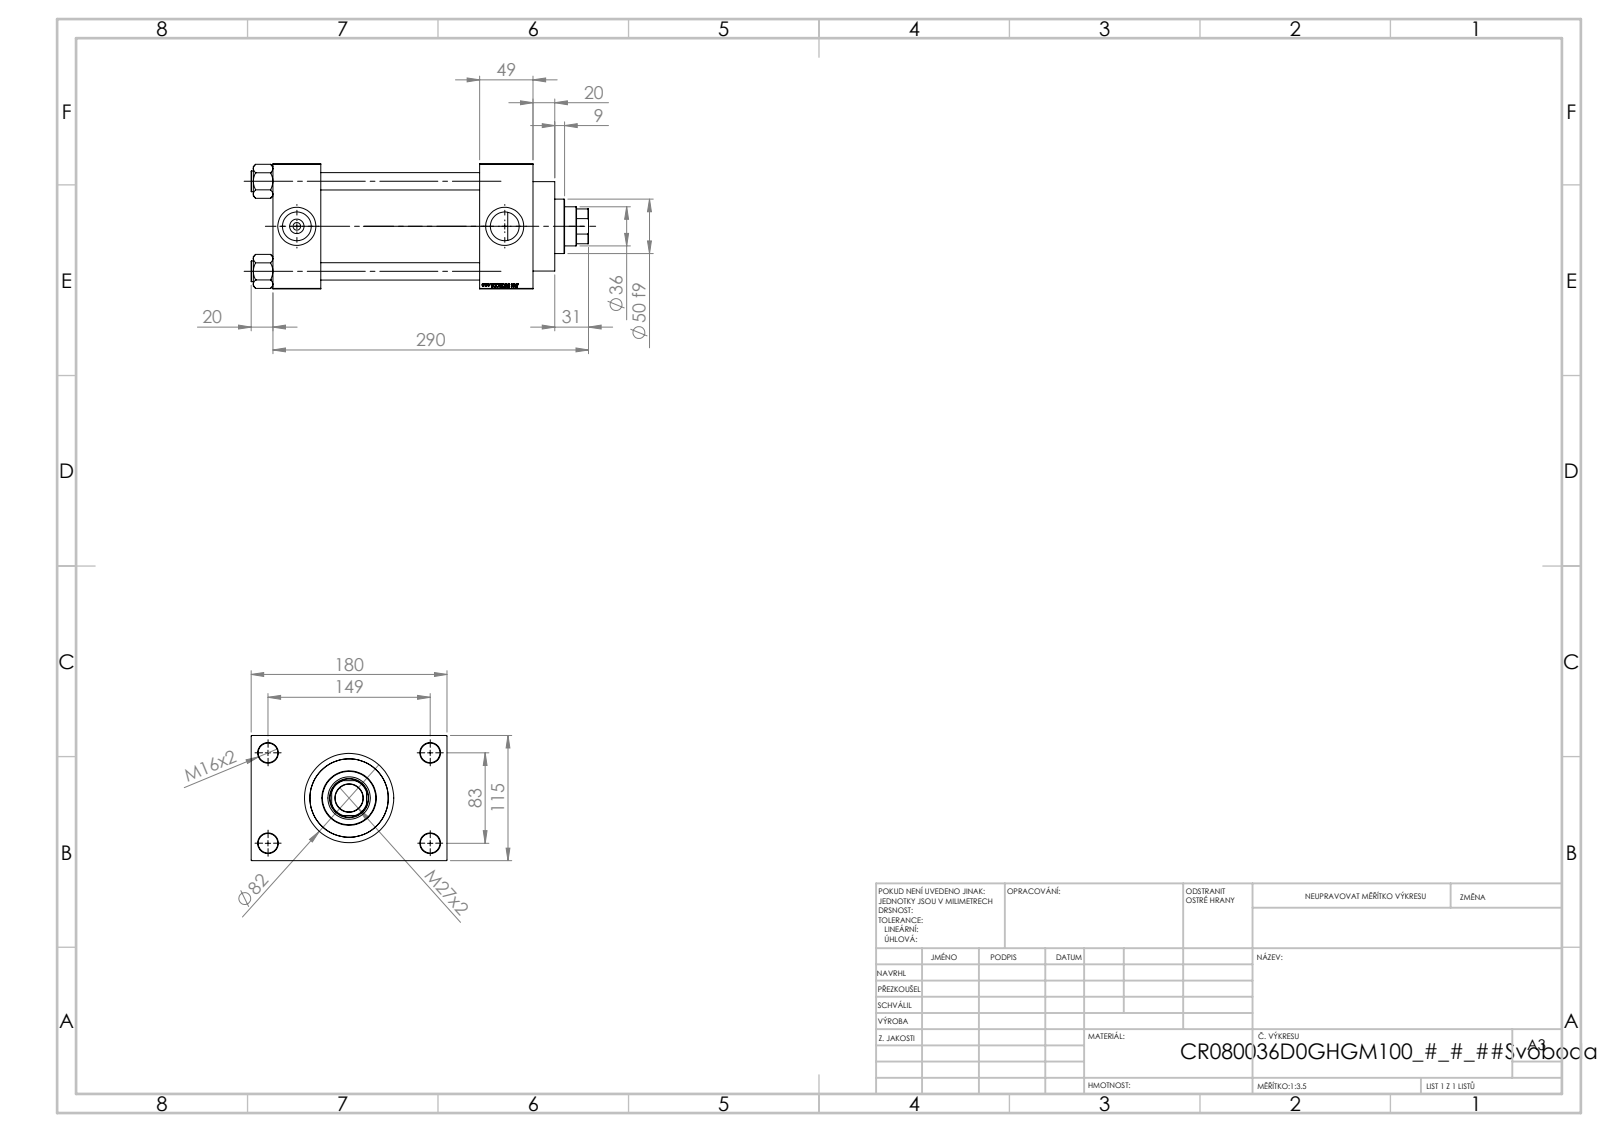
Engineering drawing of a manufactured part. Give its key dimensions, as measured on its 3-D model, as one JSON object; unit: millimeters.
{"part_name": "NUT_M5_D; V215CR_VCP_D; V215_VC_A; V215CR_D_TYCINKA (+1 more)", "step_written_by": "SolidWorks 2019 (CONFIG_CONTROL_DESIGN)", "units": "millimeters", "bodies": {"solids": 11, "faces": 1151, "planar": 545, "cylindrical": 88, "other": 518}, "overall_size": [310, 180, 115], "volume_mm3": 2188000, "surface_area_mm2": 363447, "round_holes": [[16, 4], [18, 4], [7, 2], [26.44, 2], [35, 2], [25.5, 1], [36, 1], [39, 1], [61, 1], [72, 1], [80, 1]], "round_bosses_or_shafts": [[19, 4], [86, 1], [82, 1], [50, 1]], "partial_cylinders_radius": [[17.5, 1]], "face_to_face_distances": [115, 146, 195, 49, 44, 190, 239, 32.5, 147.5, 180], "hole_center_spacings": [33.15, 58.48, 82.7, 85.28, 89.24, 115.85, 142.43, 83]}
